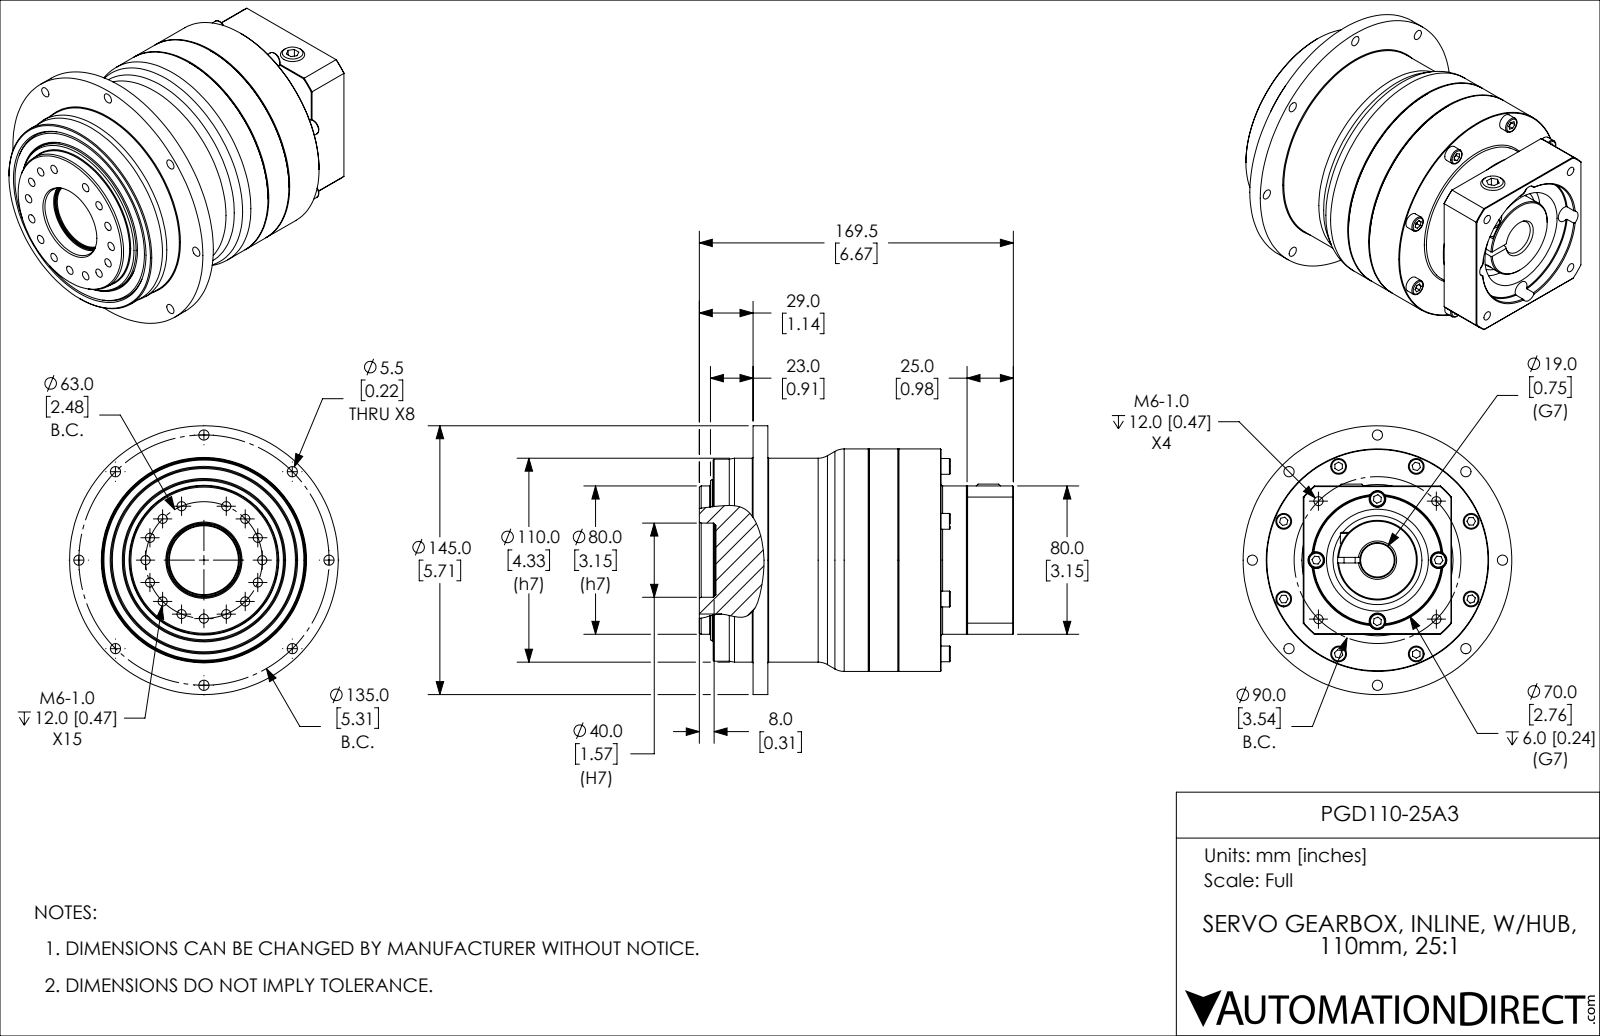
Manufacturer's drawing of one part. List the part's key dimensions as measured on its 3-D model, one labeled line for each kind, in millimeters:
Part name (STEP PRODUCT): PGD110-25A3
STEP written by: SolidWorks 2015 (AUTOMOTIVE_DESIGN)
Units: millimetres
Bodies: 5 solids, 493 faces (230 planar, 184 cylindrical, 79 other)
Overall size (bounding box): 169.5 × 145 × 145
Volume: 1 477 000 mm³ · Surface area: 132 313 mm²
Round holes (diameter × count): ⌀4.92 ×14, ⌀5.5 ×8, ⌀4.92 ×5, ⌀9 ×4, ⌀6 ×1, ⌀10 ×1, ⌀10.5 ×1, ⌀19 ×1, ⌀37.2 ×1, ⌀39.2 ×1, ⌀48 ×1, ⌀55 ×1
Round bosses / shafts (diameter × count): ⌀8.5 ×12, ⌀6 ×3, ⌀145 ×1, ⌀120 ×1, ⌀110 ×1, ⌀80 ×1, ⌀42 ×1, ⌀40 ×1
Partial cylindrical surfaces — rounded edges, fillets, slot ends (radius × count): R5.5 ×1, R52.5 ×1
Main face-to-face distances: 4, 22, 126.5, 104.5, 100.5, 26, 133.5, 2, 11, 115.5
Hole centre spacings: 40.25, 62.62, 84.71, 97.35, 12.29, 52.38, 74.49, 44.54
